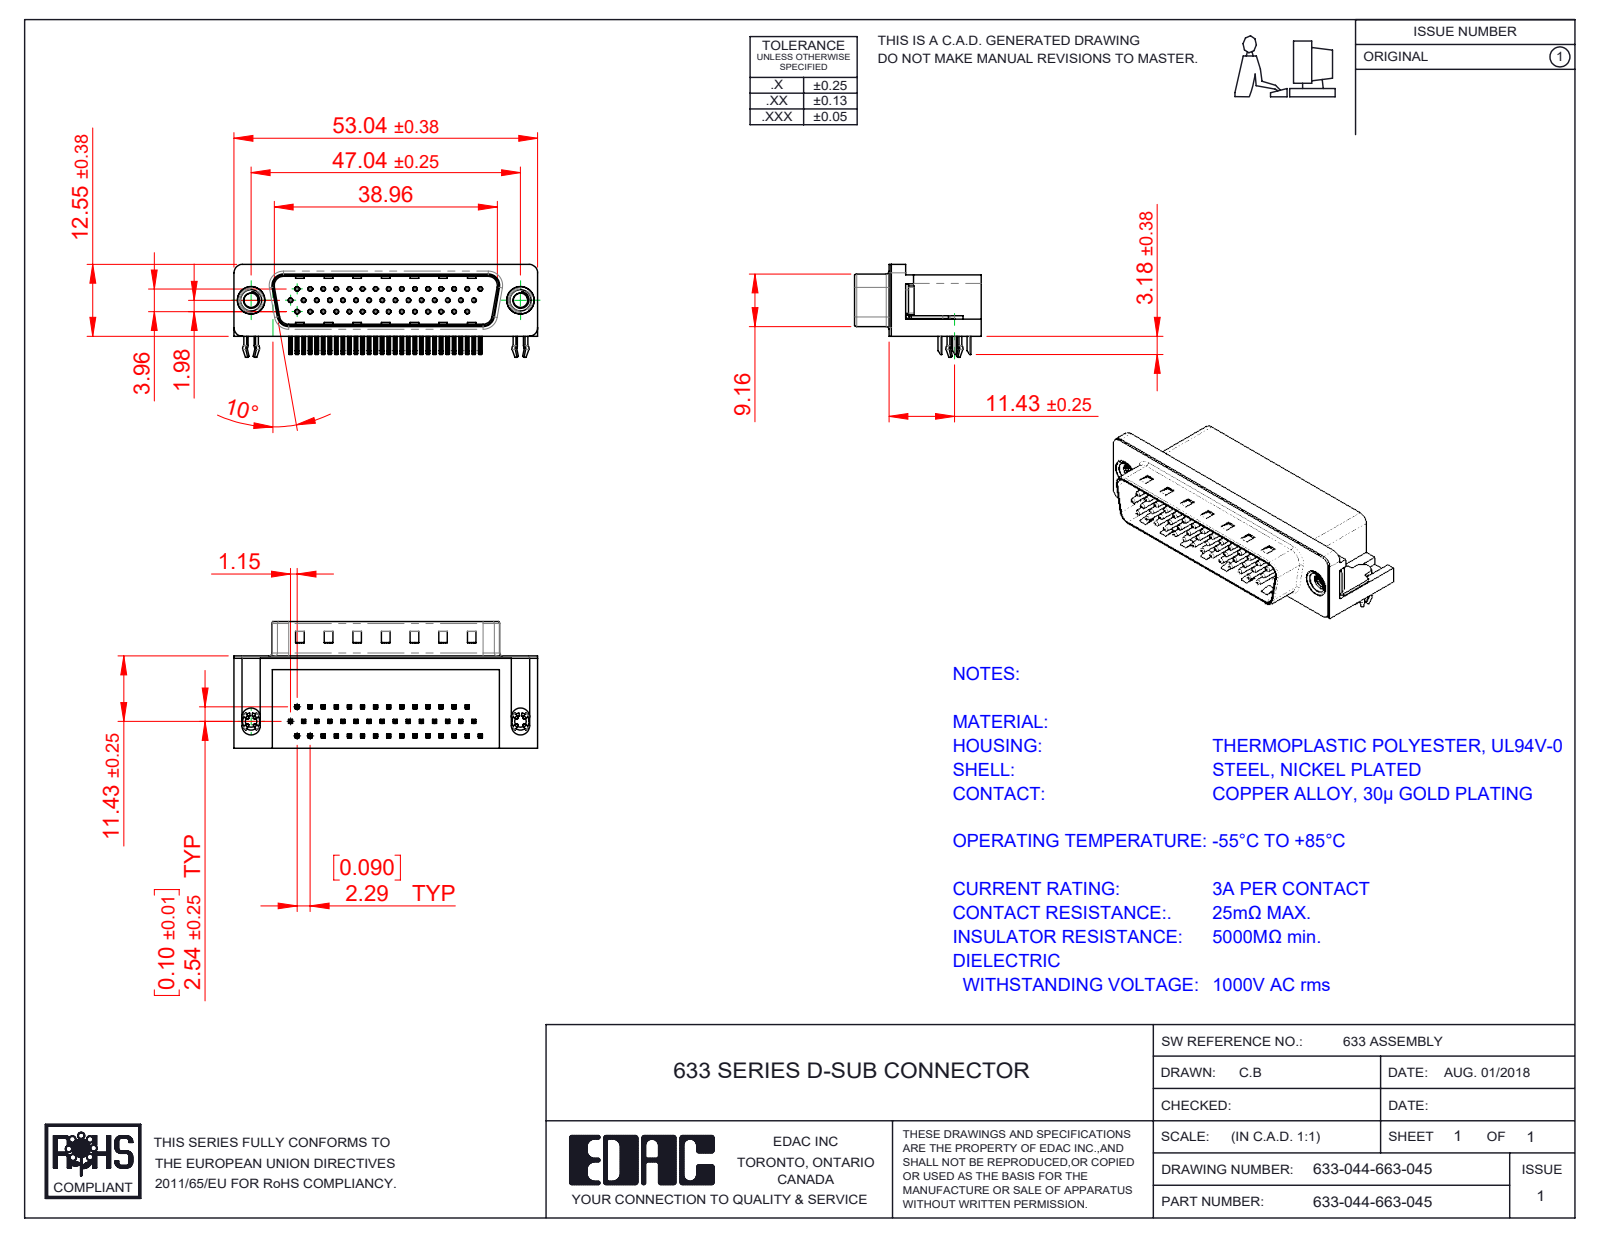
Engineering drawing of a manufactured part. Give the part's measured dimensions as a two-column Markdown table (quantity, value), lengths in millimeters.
| quantity | value |
| --- | --- |
| part name | 633 Contact Top; 633-044-663-045; 633 Contact Bottom; 633 Housing_44 Contact (+4 more) |
| STEP written by | SolidWorks 2016 (CONFIG_CONTROL_DESIGN) |
| units | millimeters |
| bodies | 50 solids, 3810 faces (2359 planar, 1070 cylindrical, 381 other) |
| overall size | 53.04 × 22.1 × 16.25 |
| volume | 8 119 mm³ |
| surface area | 10 296 mm² |
| round holes (diameter × count) | 0.35 × 44, 0.8 × 44, 2 × 2, 2.5 × 2, 4 × 2, 4.8 × 2, 5 × 2 |
| round bosses / shafts (diameter × count) | 0.75 × 44, 4.9 × 2, 4.75 × 2, 3.9 × 2, 3 × 2 |
| partial cylindrical surfaces (radius × count) | 0.25 × 188, 0.12 × 88, 1 × 16, 0.5 × 9, 1.6 × 8, 1.5 × 7, 0.9 × 4, 2 × 4 |
| main face-to-face distances | 0.4, 10.35, 15.7, 2.9, 8.76, 2.5, 2.1, 16.1, 10.7, 2.54 |
| hole center spacings | 2.29, 4.57, 4.58, 2.28, 6.87, 9.16, 11.45, 2.27 |
